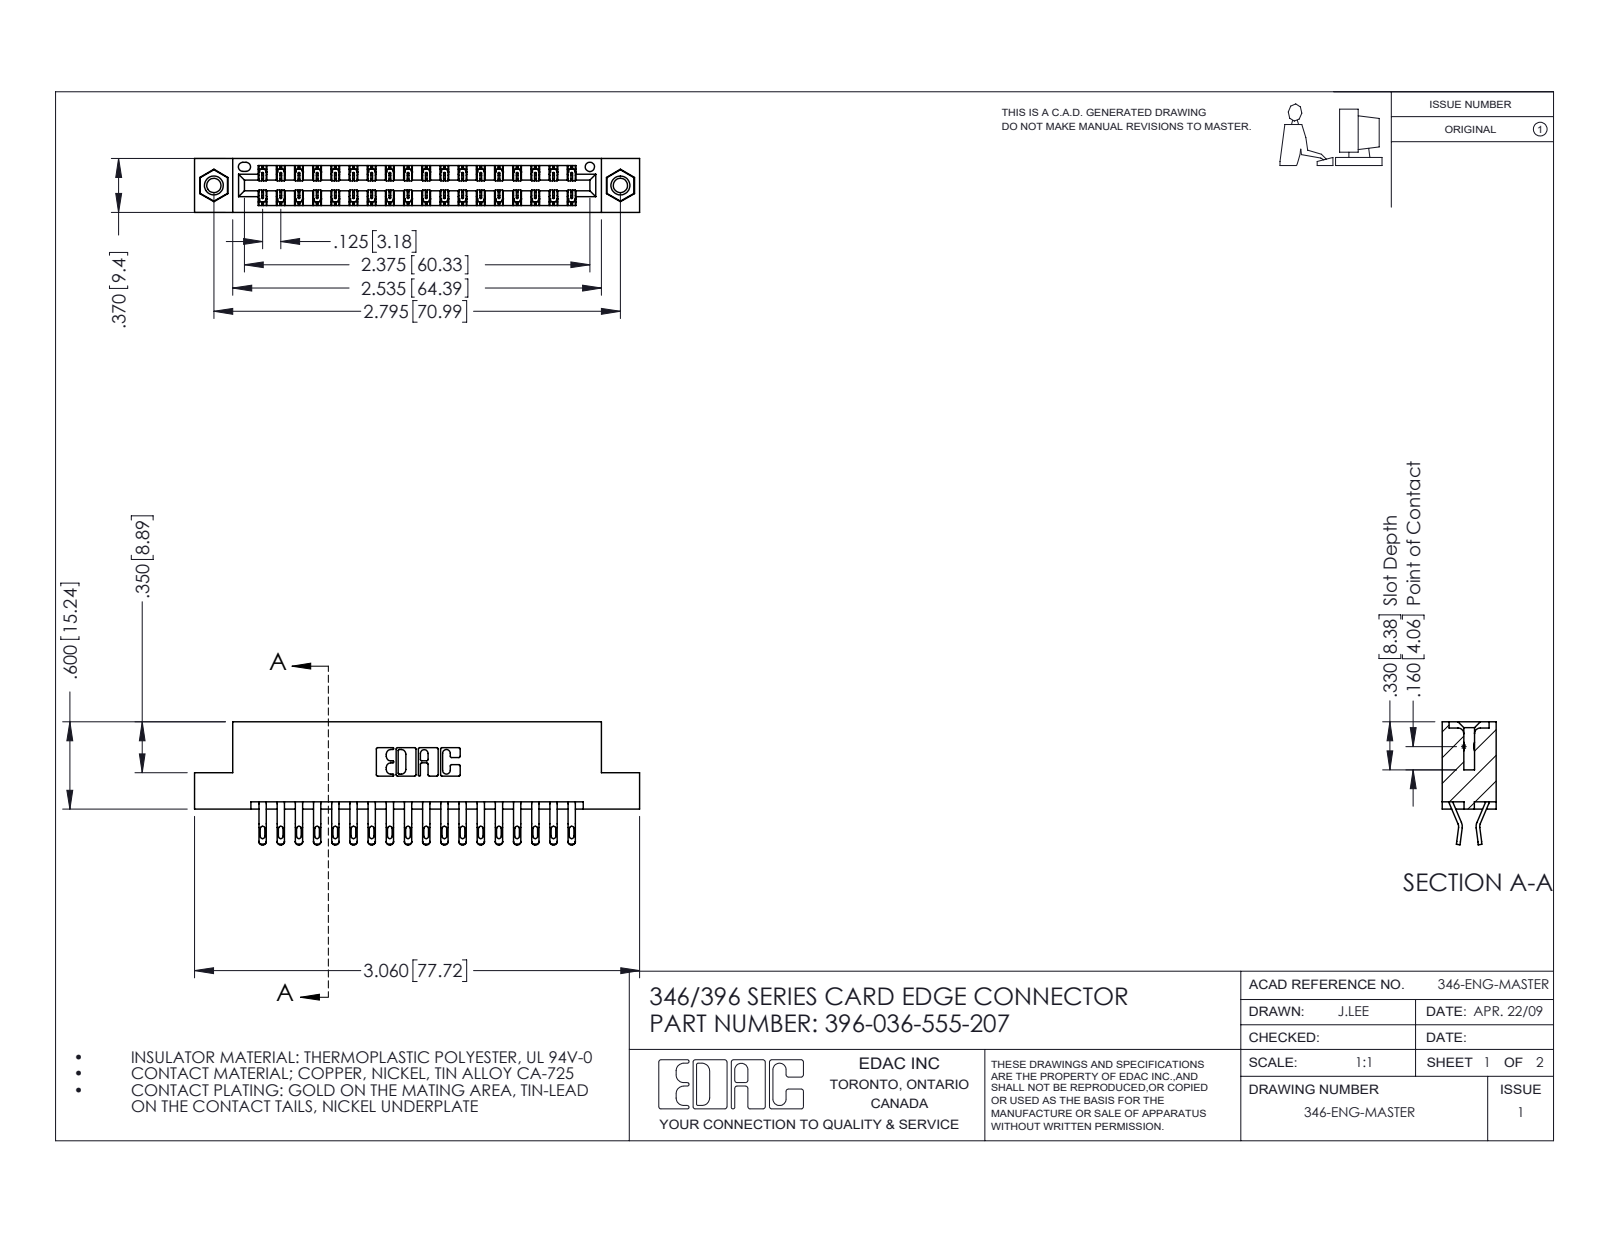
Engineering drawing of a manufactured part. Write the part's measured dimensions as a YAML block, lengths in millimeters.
part_name: "345-292-001_555 Tail; 396-036-555-207; 345-250-001_345-250-005-103; 346 Part_Flush Mounting Lugs - 0.156 Dia-TI"
step_written_by: "SolidWorks 2016 (CONFIG_CONTROL_DESIGN)"
units: millimeters
bodies: {solids: 39, faces: 2270, planar: 1296, cylindrical: 958, other: 16}
overall_size: [77.7, 21.5, 9.4]
volume: 7490
surface_area: 10320
round_holes:
  - {diameter: 2.5, count: 2}
  - {diameter: 3.2, count: 2}
  - {diameter: 4, count: 2}
  - {diameter: 1.6, count: 1}
round_bosses_or_shafts:
  - {diameter: 3.9, count: 2}
partial_cylinders:
  - {radius: 0.4, count: 72}
  - {radius: 0.5, count: 72}
  - {radius: 0.2, count: 54}
  - {radius: 0.3, count: 22}
  - {radius: 0.2, count: 6}
  - {radius: 0.8, count: 6}
  - {radius: 0.7, count: 3}
  - {radius: 0.3, count: 2}
face_to_face_distances: [1.2, 8.2, 6.4, 9.4, 0.6, 1.8, 7.6, 7, 3.8, 5.6]
hole_center_spacings: [6.2, 65.7, 71]
